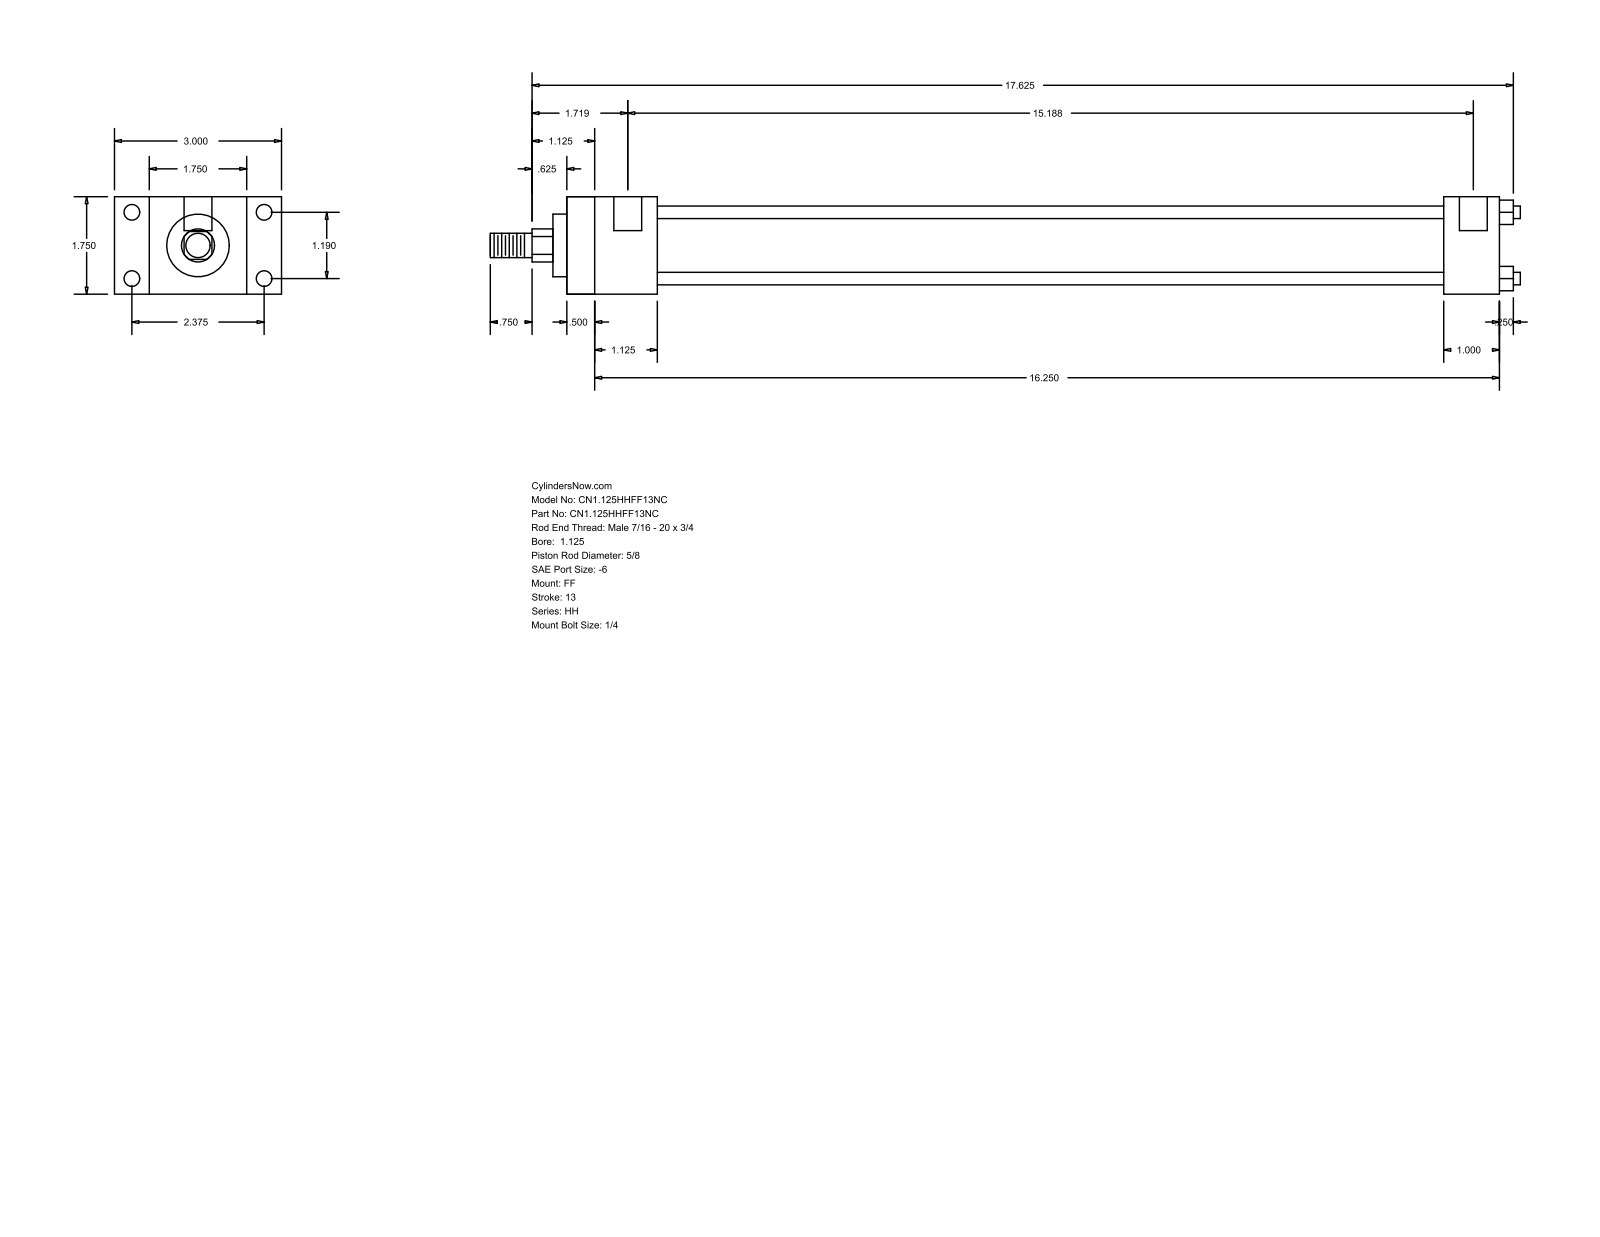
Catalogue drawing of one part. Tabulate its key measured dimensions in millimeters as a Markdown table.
| quantity | value |
| --- | --- |
| part name | HH_FF__0112_0.625 |
| STEP written by | GSSL Pune (CONFIG_CONTROL_DESIGN) |
| units | millimeters |
| bodies | 0 solids, 92 faces (64 planar, 28 cylindrical, 0 other) |
| overall size | 469.9 × 76.2 × 44.45 |
| round holes (diameter × count) | 5.56 × 4, 7.14 × 4, 12.7 × 2 |
| round bosses / shafts (diameter × count) | 5.71 × 4, 34.92 × 1, 28.57 × 1, 15.88 × 1, 11.11 × 1 |
| partial cylindrical surfaces (radius × count) | 7.54 × 1 |
| main face-to-face distances | 44.46, 425.44, 15.87, 12.69, 412.75, 28.58, 60.33, 41.27, 400.05, 387.36 |
| hole center spacings | 30.22, 60.32, 67.47, 382.59, 3.17, 385.76 |
